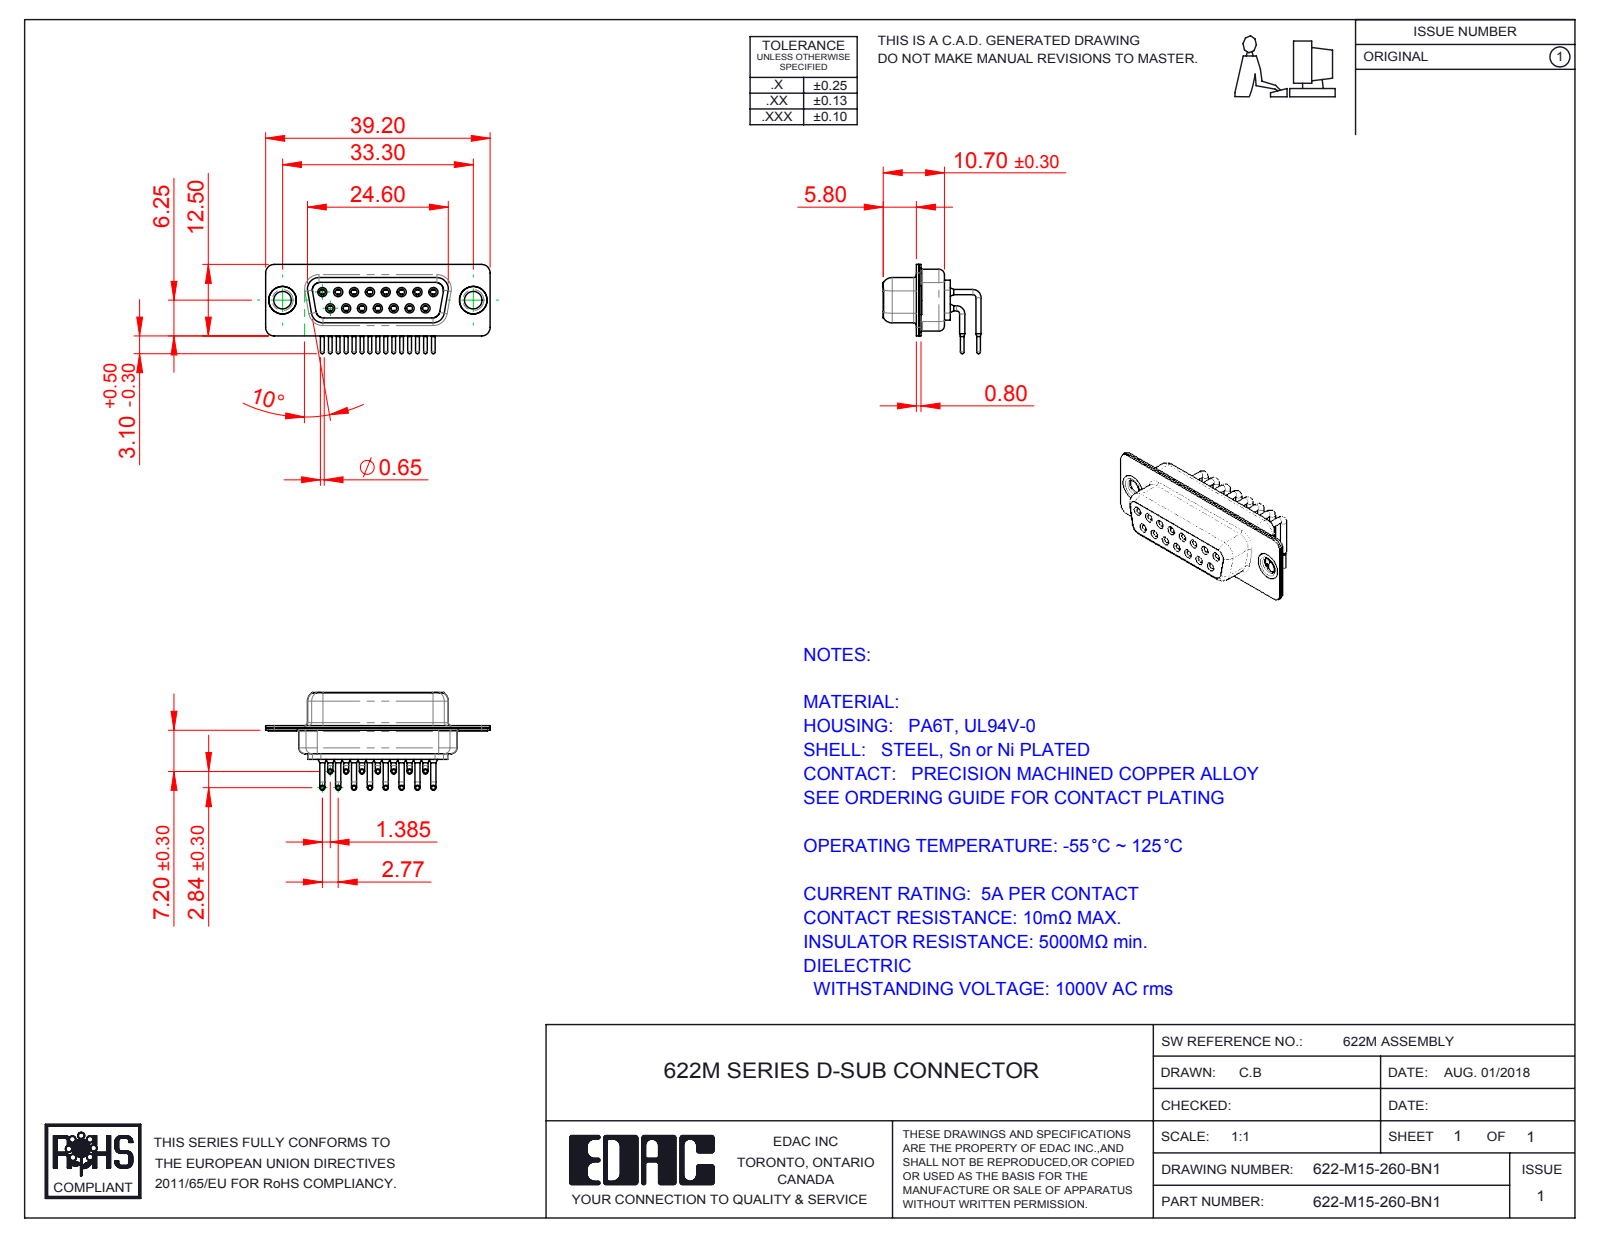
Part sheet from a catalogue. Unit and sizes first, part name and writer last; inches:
Units: inches
Overall size (bounding box): 1.543 × 0.673 × 0.614
Round holes (diameter × count): ⌀0.039 ×15, ⌀0.043 ×15, ⌀0.067 ×15, ⌀0.071 ×15, ⌀0.079 ×15, ⌀0.12 ×2, ⌀0.157 ×2, ⌀0.189 ×2
Round bosses / shafts (diameter × count): ⌀0.035 ×30, ⌀0.063 ×15, ⌀0.059 ×15, ⌀0.026 ×15, ⌀0.197 ×2, ⌀0.193 ×2, ⌀0.14 ×2
Partial cylindrical surfaces — rounded edges, fillets, slot ends (radius × count): R0.059 ×16, R0.079 ×12, R0.053 ×8, R0.063 ×8, R0.01 ×4, R0.02 ×4, R0.024 ×4, R0.026 ×4
Main face-to-face distances: 0.016, 0.057, 0.352, 0.244, 0.075, 0.335, 0.091, 0.018, 0.278, 0.033
Hole centre spacings: 0.124, 0.109, 0.218, 0.327, 0.436, 0.198, 0.198, 0.294
Volume: 0.15 in³ · Surface area: 9.715 in²
Bodies: 20 solids, 1048 faces (292 planar, 466 cylindrical, 290 other)
Part name (STEP PRODUCT): 622M Shell Rear_15 Contacts; 622M Shell Front_15 Contacts; 622M Housing_15 Contacts; 622M Thru Hole Rivet (+3 more)
STEP written by: SolidWorks 2016 (CONFIG_CONTROL_DESIGN)
